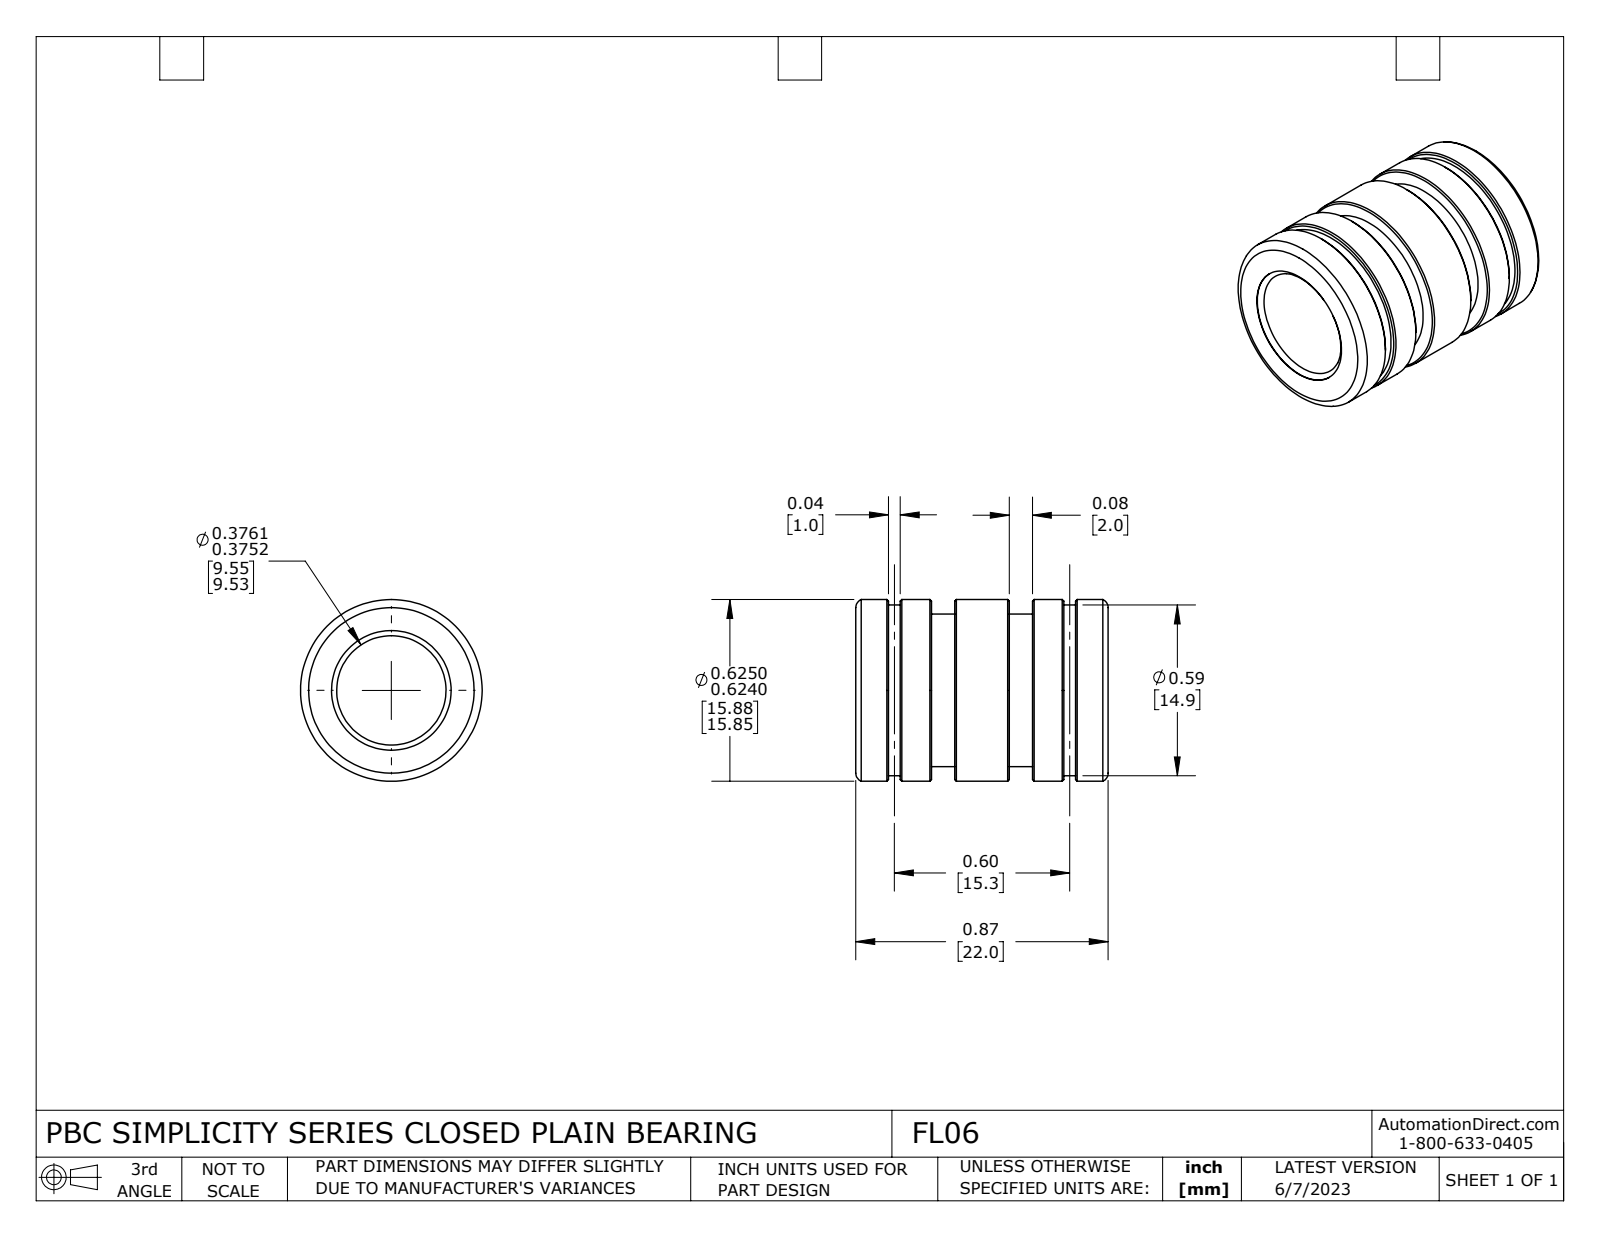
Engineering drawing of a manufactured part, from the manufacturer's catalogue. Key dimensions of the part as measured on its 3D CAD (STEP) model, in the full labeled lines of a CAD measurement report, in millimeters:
Part name (STEP PRODUCT): FL06
STEP written by: SolidWorks 2021 (CONFIG_CONTROL_DESIGN)
Units: millimetres
Bodies: 2 solids, 58 faces (10 planar, 24 cylindrical, 24 other)
Overall size (bounding box): 22 × 15.8 × 15.8
Volume: 2 470 mm³ · Surface area: 3 663 mm²
Round holes (diameter × count): ⌀9.6 ×1, ⌀10.4 ×1
Round bosses / shafts (diameter × count): ⌀15.8 ×1, ⌀14.9 ×1, ⌀13.3 ×1
Main face-to-face distances: 6.6, 8.7, 13.4, 15.4, 2, 6.8, 22, 8.8, 4.7, 3.9
